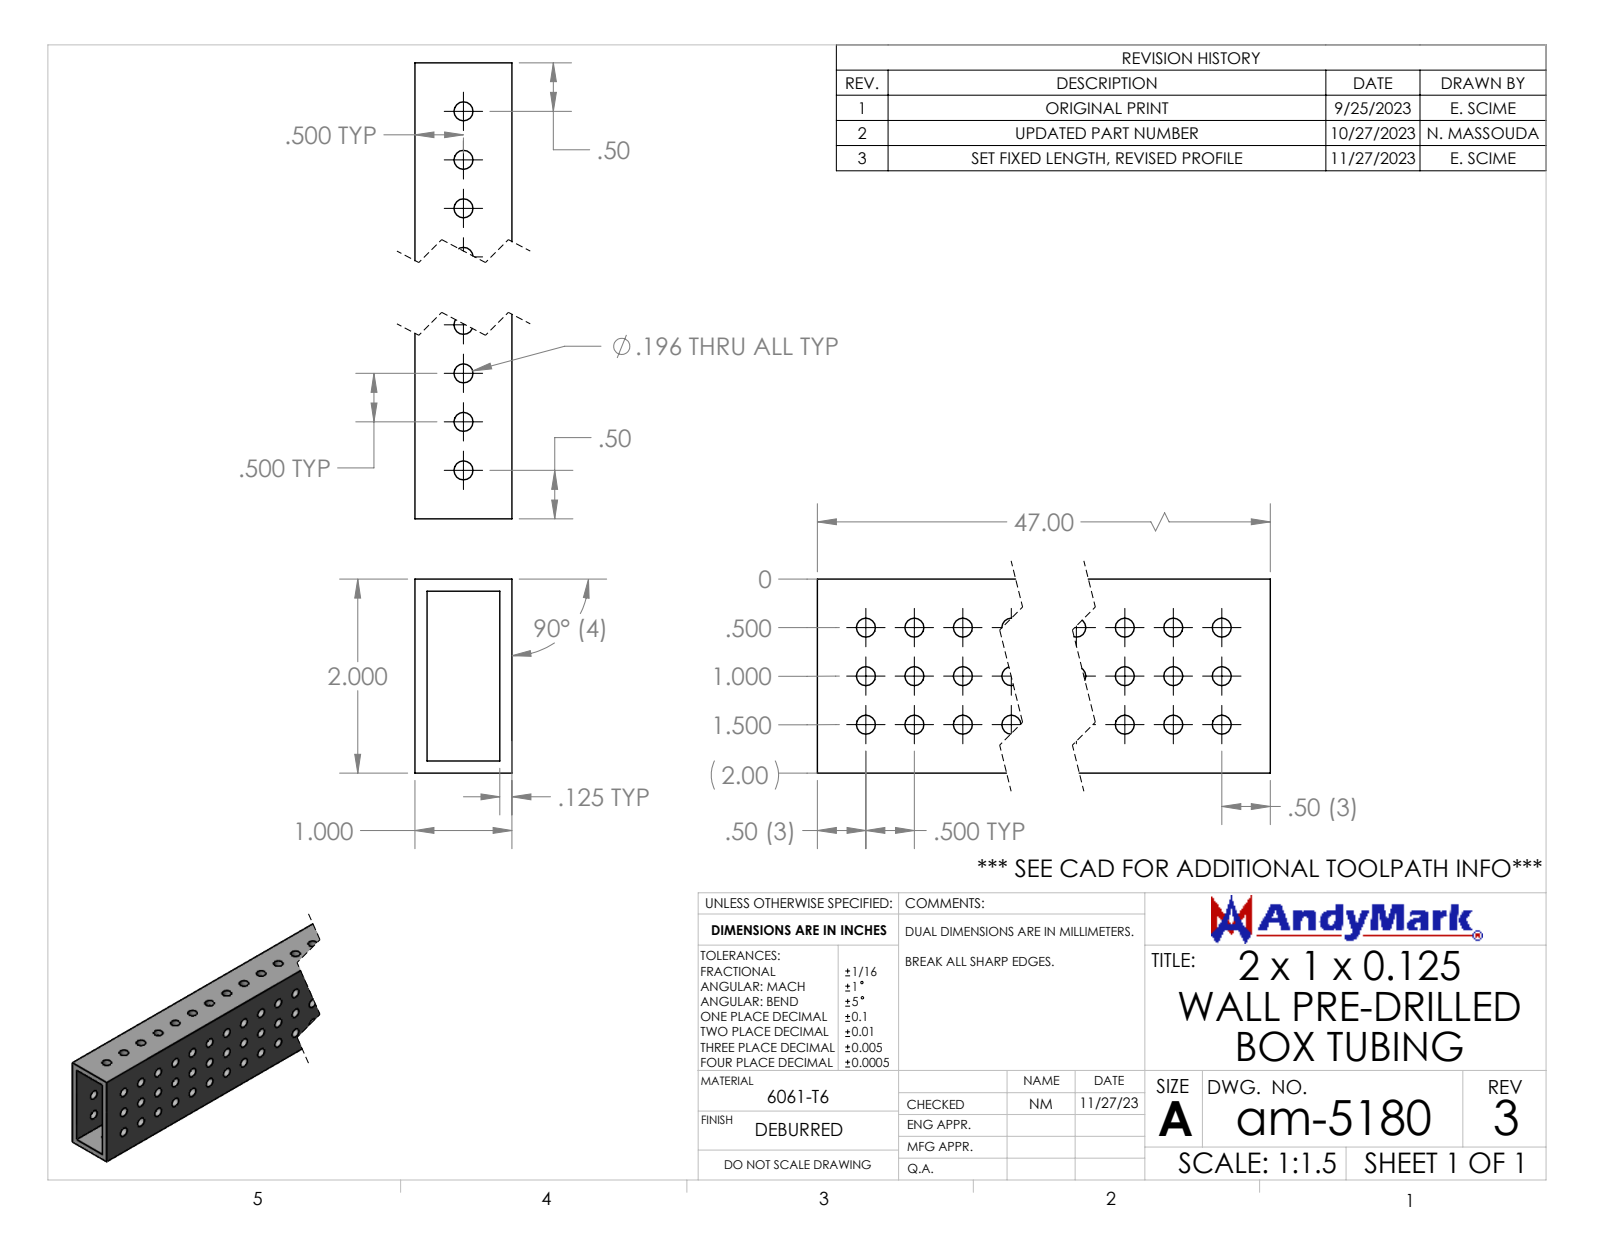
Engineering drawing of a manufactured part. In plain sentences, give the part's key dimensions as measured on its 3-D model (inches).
The part is named "am-5180 2x1x0.125 Wall Pre-Drilled Box Tube". Its 3-D file was written by "SolidWorks 2024 (AUTOMOTIVE_DESIGN)". It is 1 solid with 1498 faces: 10 planar, 1488 cylindrical and 0 other. Overall it measures 47 by 2 by 1 inches. Its volume is 29.51 cubic inches and its surface area 530.7 square inches. Round holes: 372 of diameter 0.196. The main face-to-face distances are 0.125, 0.875, 1, 0.75, 0.125, 1.875, 2, 1.75, 47. The hole center spacings are 0.5, 1, 1.118, 1.5, 2, 2.5, 3, 0.707.
